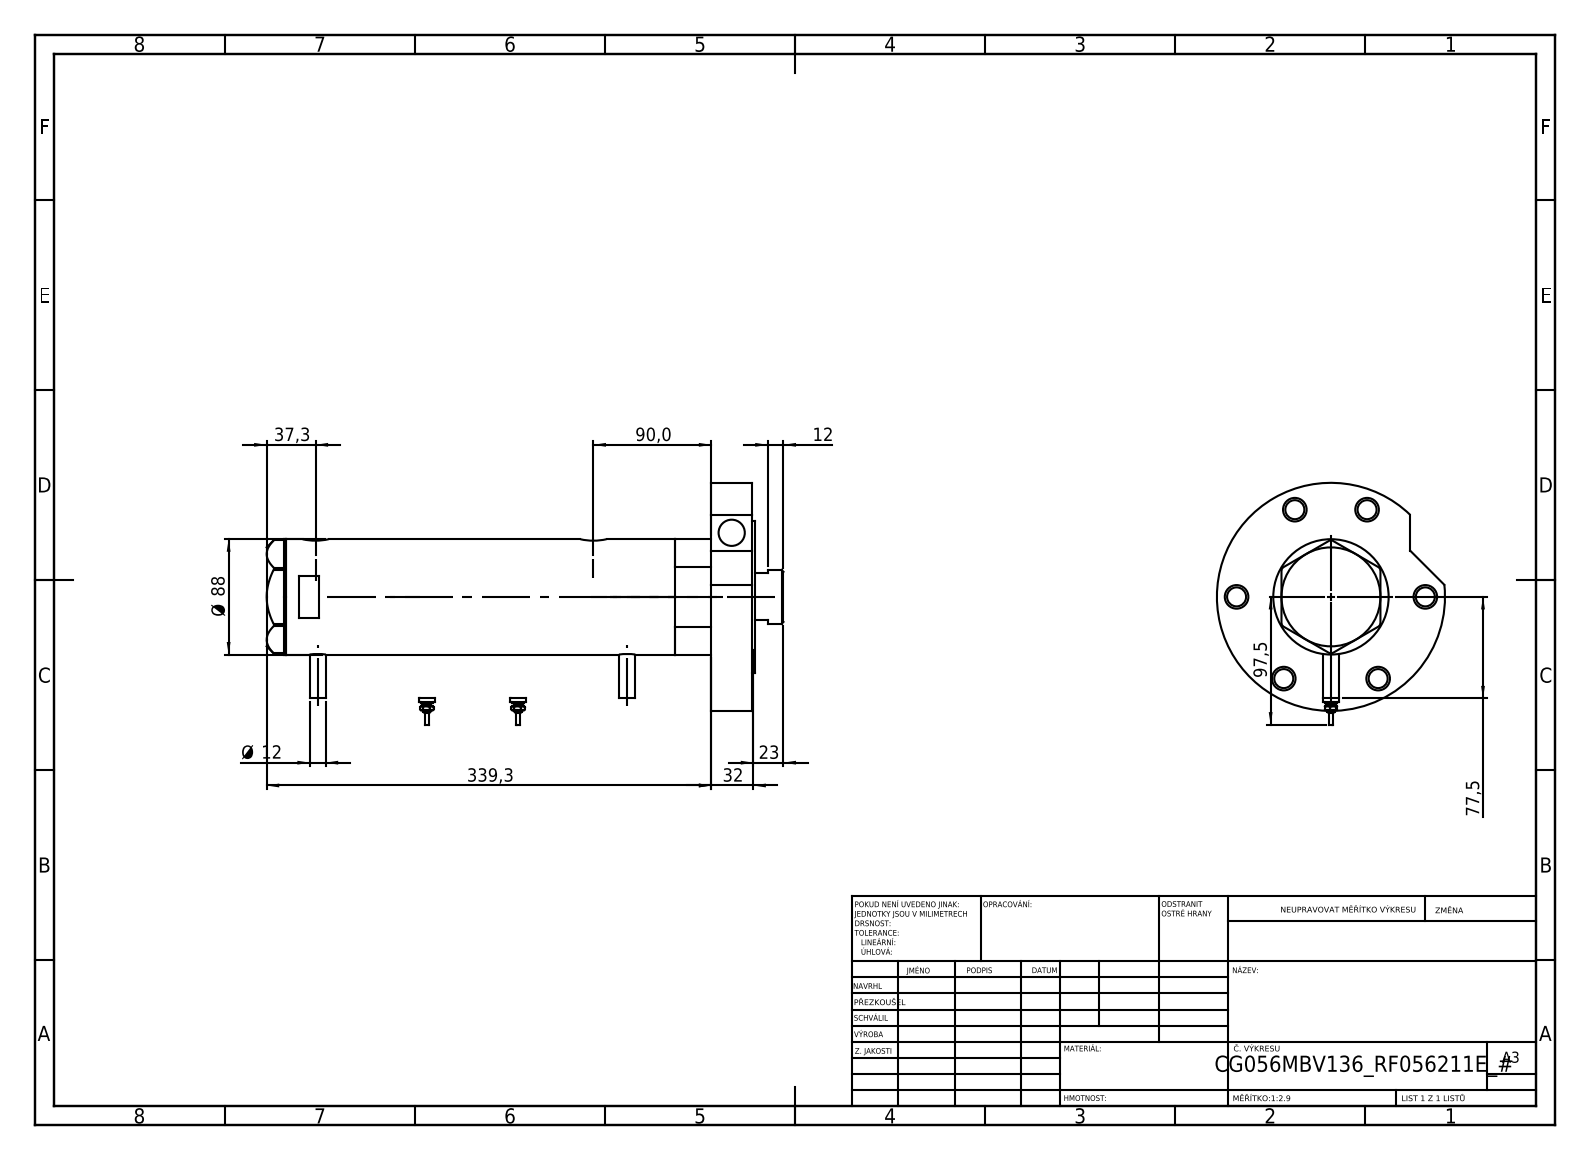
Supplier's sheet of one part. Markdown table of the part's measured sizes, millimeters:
| quantity | value |
| --- | --- |
| part name | V270CG_VC; Switch; V270CG_RF211E; V270CG_MIDDLE (+2 more) |
| STEP written by | SolidWorks 2019 (CONFIG_CONTROL_DESIGN) |
| units | millimeters |
| bodies | 7 solids, 257 faces (91 planar, 102 cylindrical, 64 other) |
| overall size | 394.3 × 184.5 × 174 |
| volume | 2 576 000 mm³ |
| surface area | 361 307 mm² |
| round holes (diameter × count) | 14.5 × 7, 18 × 6, 20 × 3, 12.5 × 2, 13.16 × 2, 42 × 1, 43.5 × 1, 56 × 1, 60 × 1, 75 × 1, 80 × 1 |
| round bosses / shafts (diameter × count) | 12 × 4, 9 × 2, 7 × 2, 4.5 × 2, 2.5 × 2, 174 × 1, 116 × 1, 88 × 1 |
| main face-to-face distances | 31, 2, 357.3, 324.3, 355.3, 33, 234.4, 89.9, 120.9, 122.9 |
| hole center spacings | 72, 80, 119.73, 124.71, 129.15, 143.69, 1.7, 25.8 |
